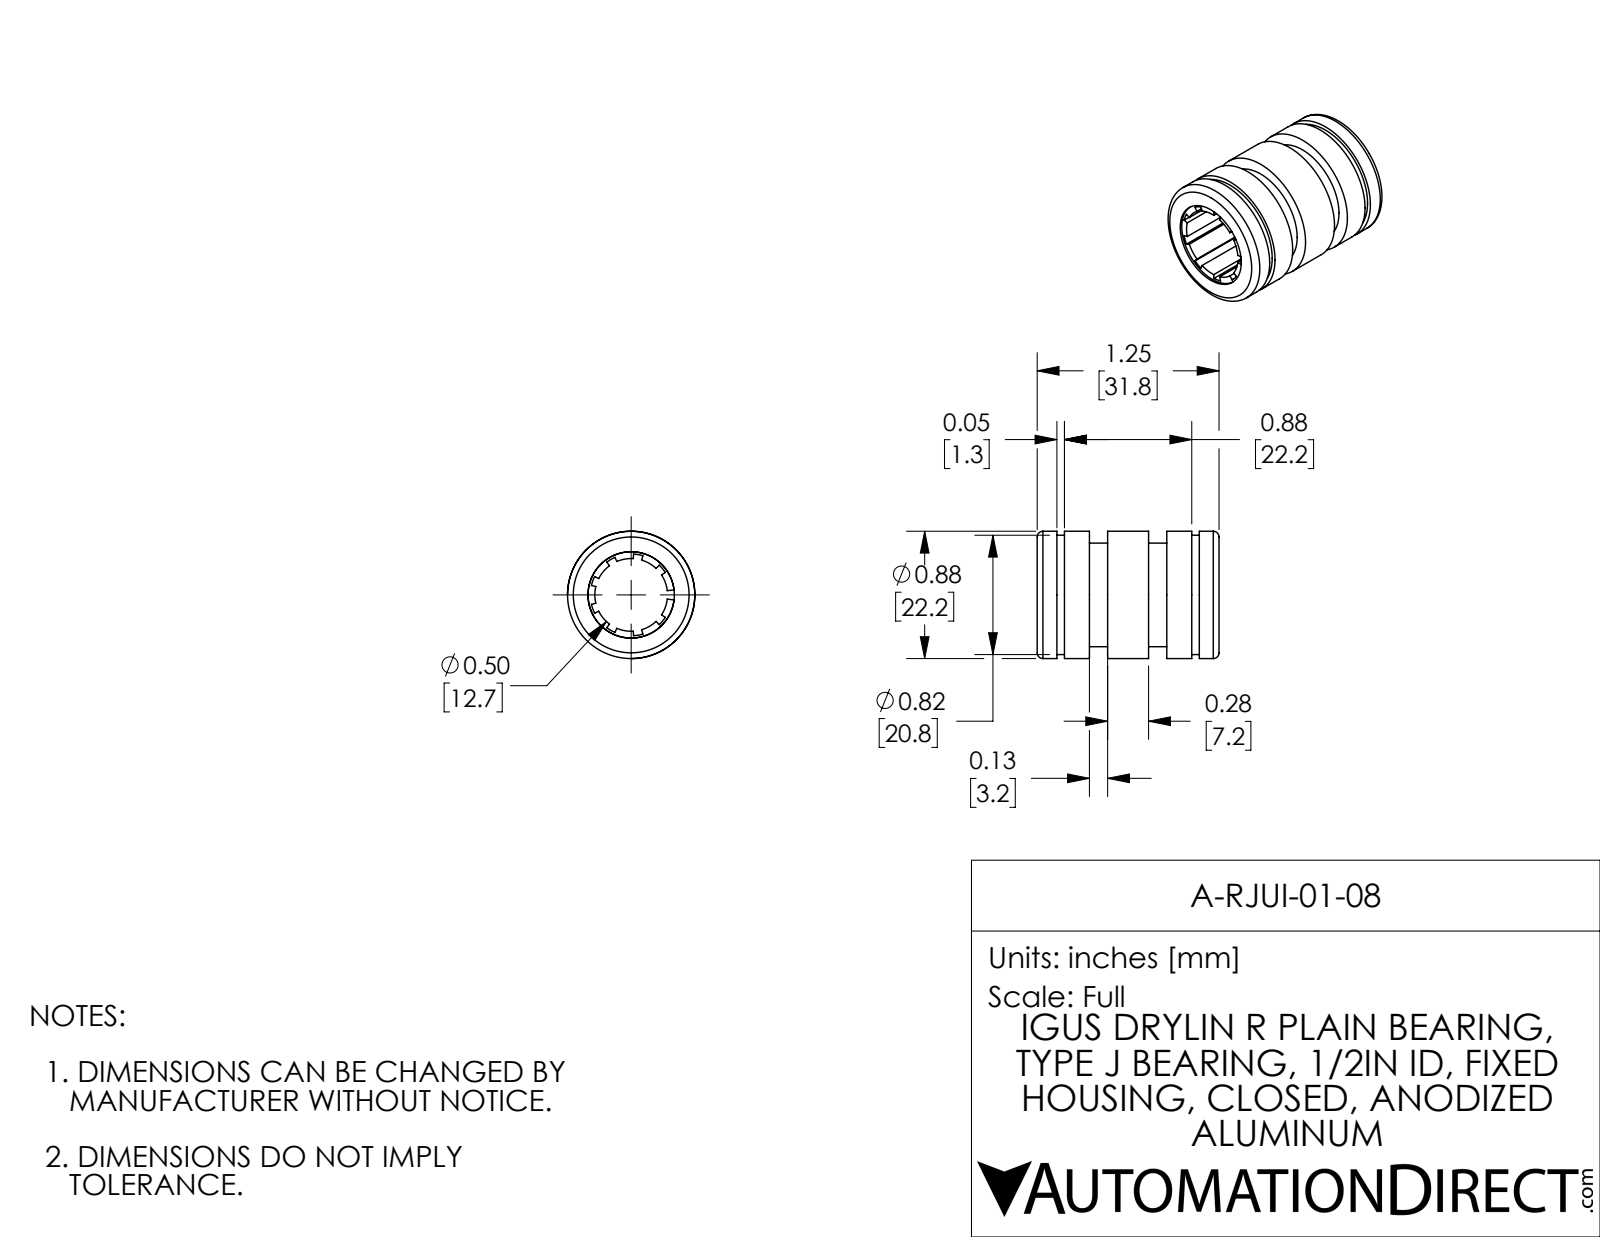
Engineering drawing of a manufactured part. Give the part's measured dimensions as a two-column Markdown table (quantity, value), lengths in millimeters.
| quantity | value |
| --- | --- |
| part name | A-RJUI-01-08 |
| STEP written by | SolidWorks 2017 (AUTOMOTIVE_DESIGN) |
| units | millimeters |
| bodies | 2 solids, 129 faces (67 planar, 58 cylindrical, 4 other) |
| overall size | 31.8 × 22.2 × 22.2 |
| volume | 6 830 mm³ |
| surface area | 8 142 mm² |
| round holes (diameter × count) | 2.8 × 1, 15.1 × 1, 17 × 1 |
| round bosses / shafts (diameter × count) | 22.2 × 1, 20.8 × 1, 18.1 × 1, 15.1 × 1, 2.6 × 1 |
| partial cylindrical surfaces (radius × count) | 6.4 × 1, 7.1 × 1, 8.3 × 1 |
| main face-to-face distances | 3.2, 5.2, 9.1, 12.3, 19.5, 22.6, 10.3, 14.3, 17.5, 8.3 |
